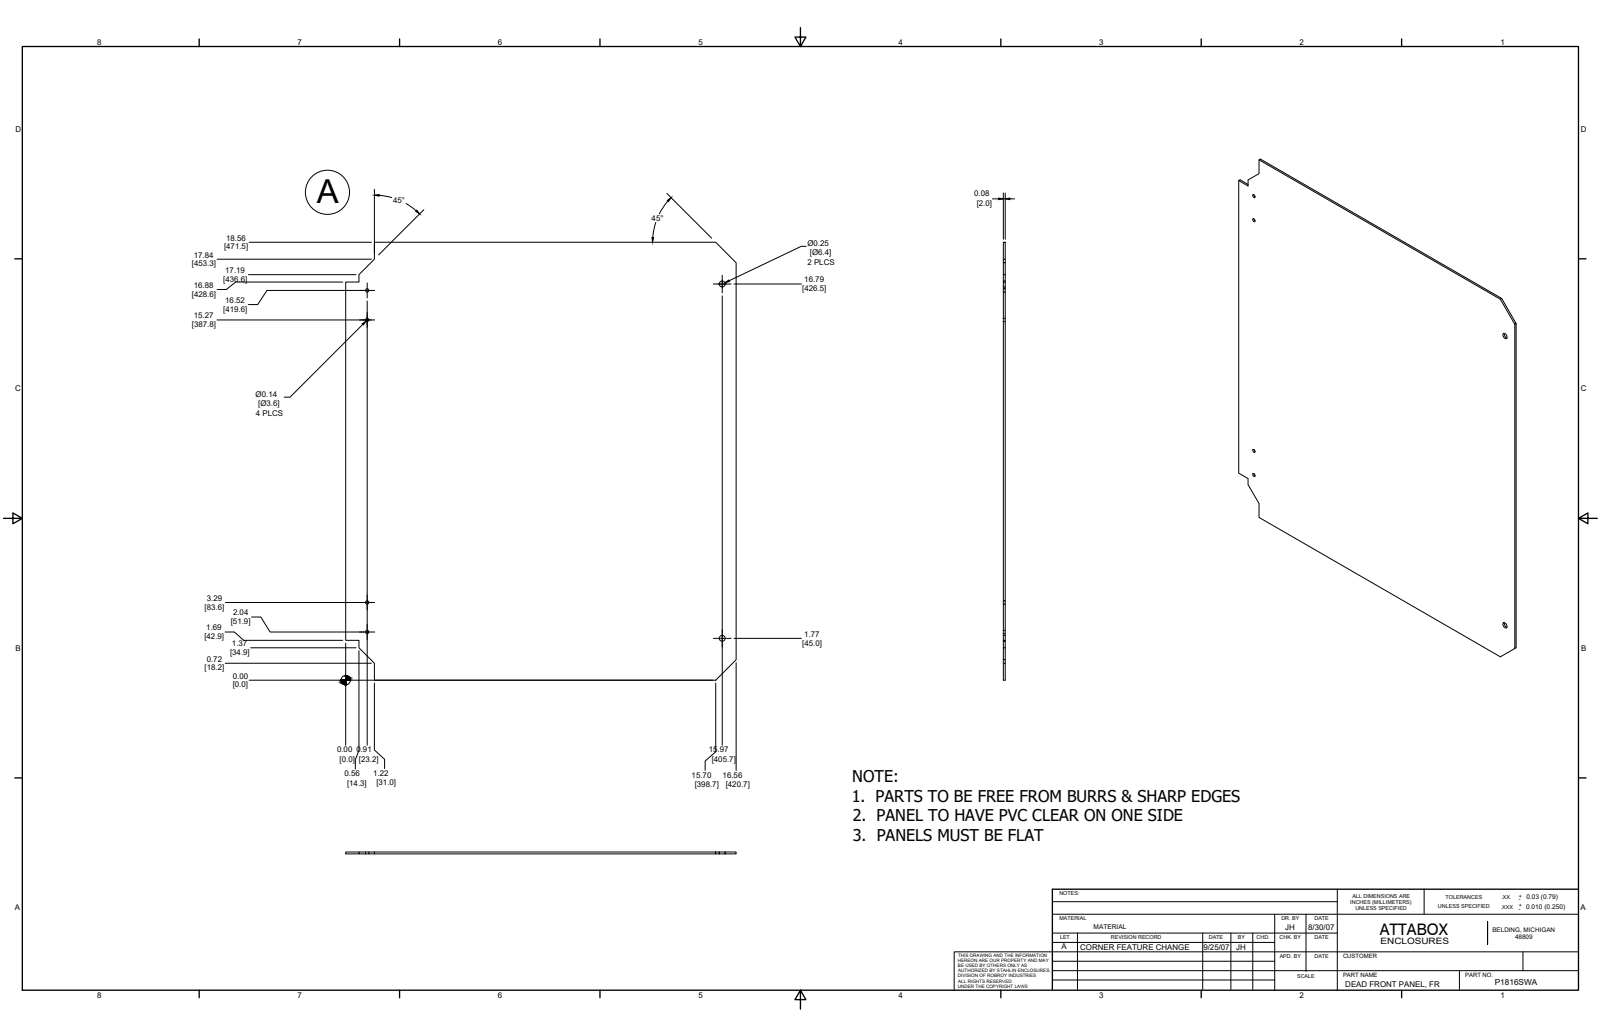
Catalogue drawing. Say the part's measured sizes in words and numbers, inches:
The part is named "P1816SWAL". Its 3-D file was written by "Autodesk Inventor 11 (AUTOMOTIVE_DESIGN)". It is 1 solid with 20 faces: 14 planar, 6 cylindrical and 0 other. Overall it measures 18.563 by 16.563 by 0.08 inches. Its volume is 24.35 cubic inches and its surface area 614.4 square inches. Round holes: 4 of diameter 0.14, 2 of diameter 0.25. The main face-to-face distances are 0.08, 16.562, 18.562, 1.09, 17.472, 15.472, 22.983, 16.383. The hole center spacings are 1.25, 13.226, 15.062, 15.137, 20.223, 21.078, 11.976, 14.476.
